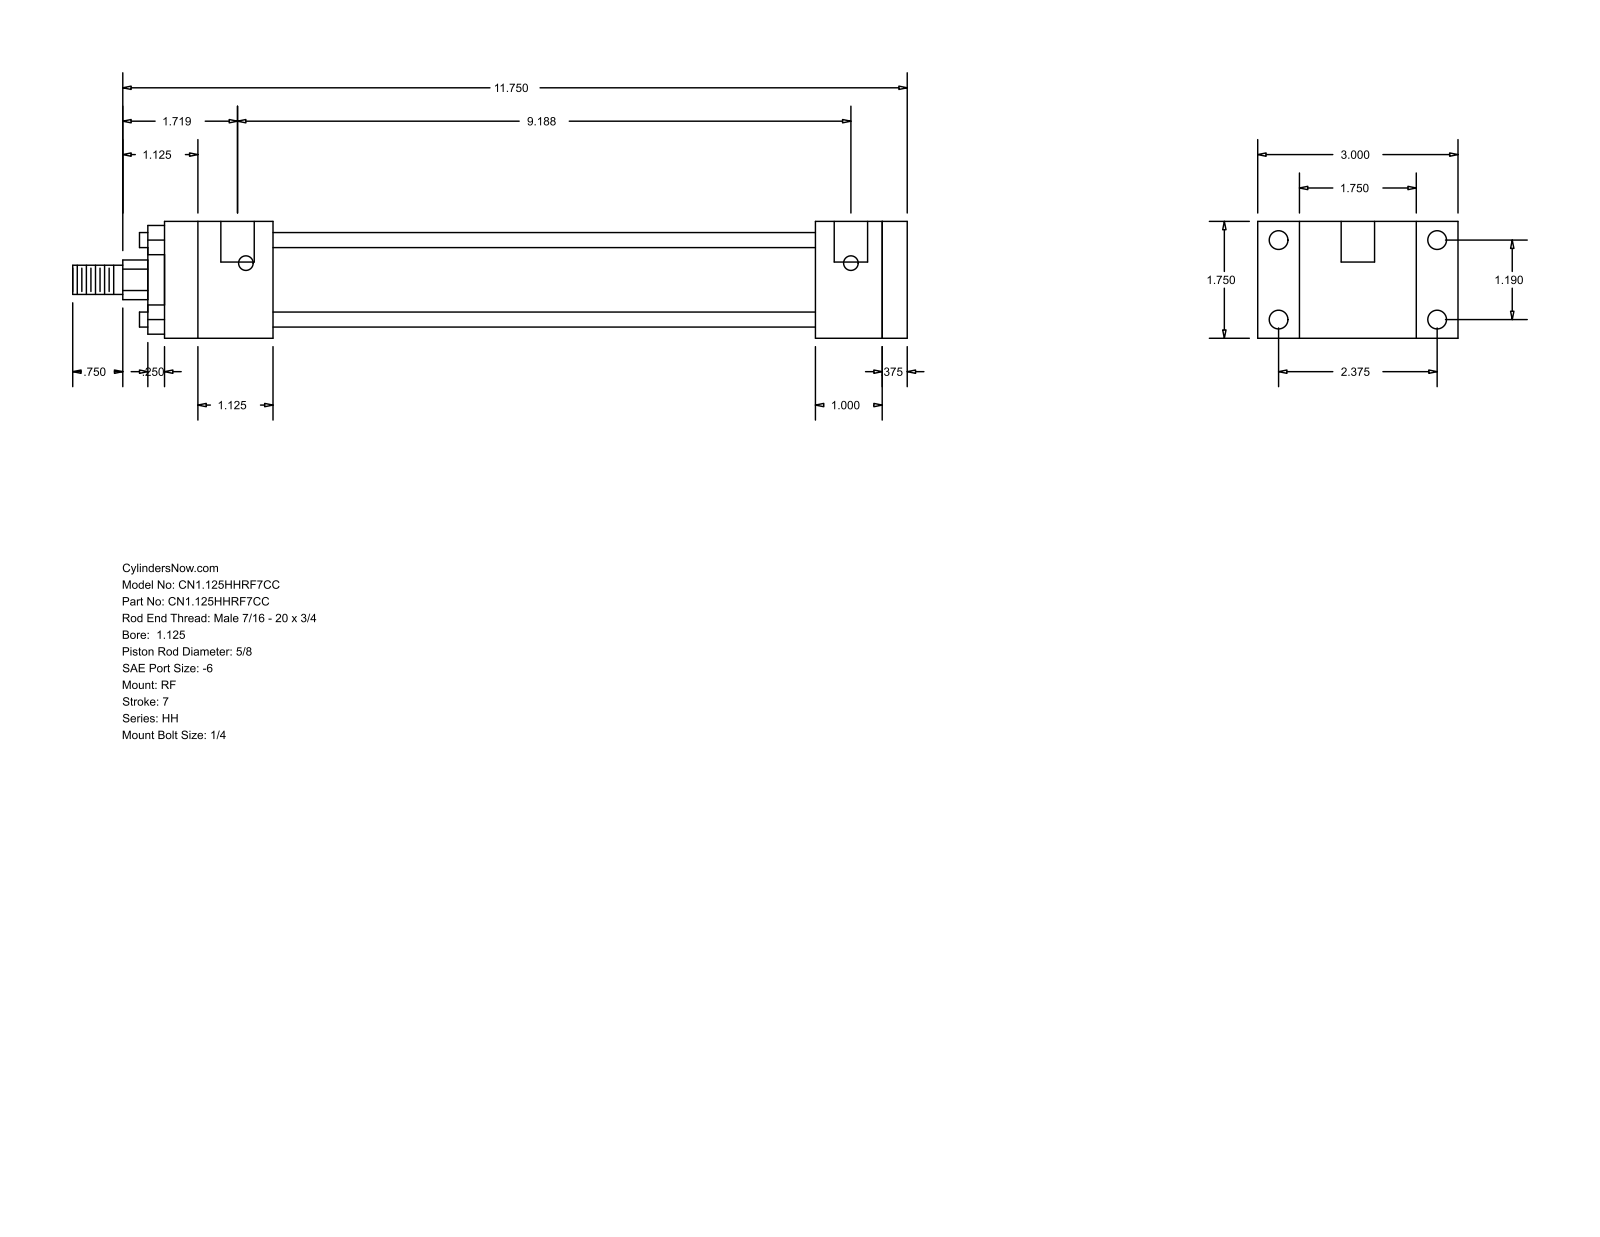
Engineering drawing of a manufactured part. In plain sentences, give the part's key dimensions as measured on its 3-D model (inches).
The part is named "HH_RF__0112_0.625". Its 3-D file was written by "GSSL Pune (CONFIG_CONTROL_DESIGN)". It is 0 solids with 92 faces: 64 planar, 28 cylindrical and 0 other. Overall it measures 12.5 by 3 by 1.75 inches. Round holes: 4 of diameter 0.219, 4 of diameter 0.281, 2 of diameter 0.5. Round bosses or shafts: 4 of diameter 0.225, 1 of diameter 1.375, 1 of diameter 1.125, 1 of diameter 0.625, 1 of diameter 0.437. Partial cylindrical surfaces (rounded edges, fillets, slot ends): 1 of radius 0.297. The main face-to-face distances are 1.75, 0.375, 1.375, 11.125, 0.625, 9.125, 9.5, 8.125, 1, 1.625. The hole center spacings are 1.19, 2.375, 2.656, 9.063, 0.125, 9.187.
